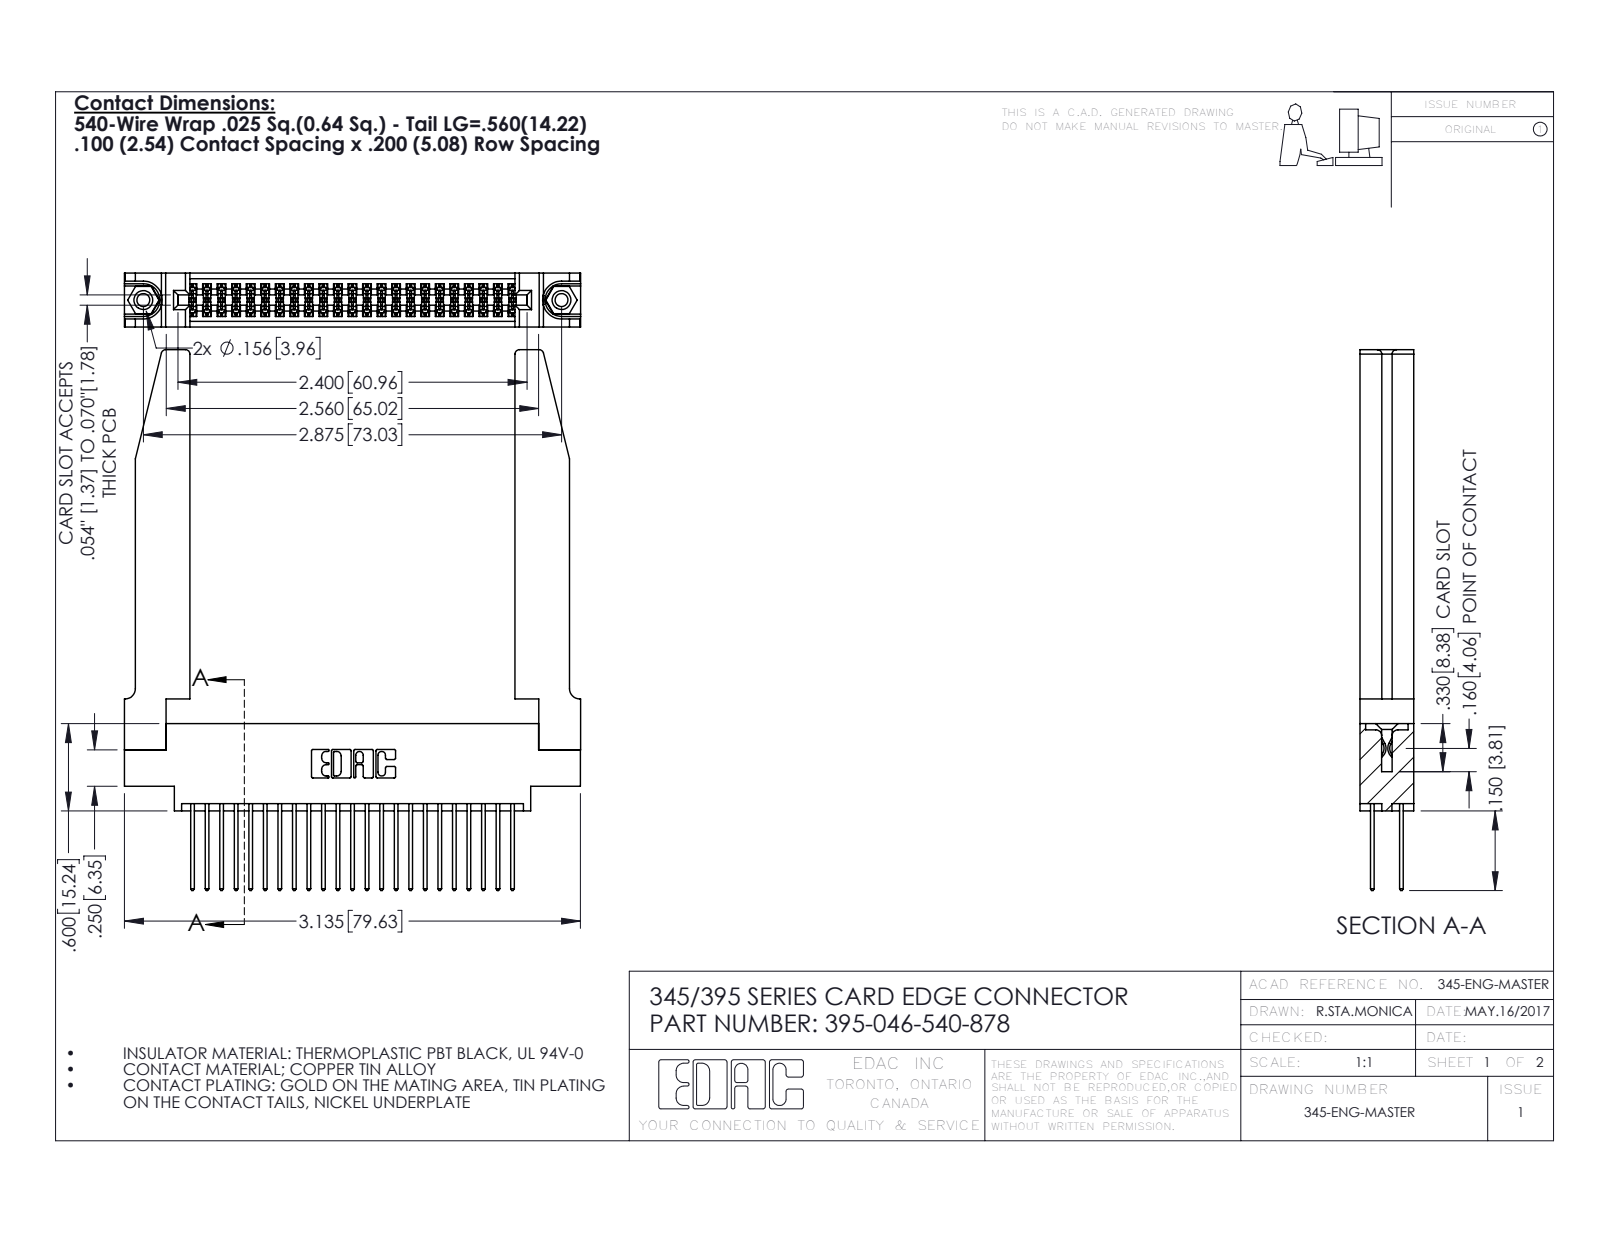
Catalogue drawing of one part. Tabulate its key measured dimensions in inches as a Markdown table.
| quantity | value |
| --- | --- |
| part name | 345-250-001_345-250-001-102; 395-046-540-878; 345-292-001_345-293-140; 345 Part_0.170 Offset - 0.156 Dia-TH (+1 more) |
| STEP written by | SolidWorks 2016 (CONFIG_CONTROL_DESIGN) |
| units | inches |
| bodies | 51 solids, 2664 faces (1744 planar, 868 cylindrical, 52 other) |
| overall size | 3.717 × 3.136 × 0.37 |
| volume | 0.939 in³ |
| surface area | 28.97 in² |
| round holes (diameter × count) | 0.089 × 2, 0.125 × 2, 0.156 × 2, 0.064 × 1 |
| round bosses / shafts (diameter × count) | 0.155 × 2 |
| partial cylindrical surfaces (radius × count) | 0.006 × 69, 0.01 × 46, 0.01 × 22, 0.03 × 8, 0.007 × 6, 0.031 × 6, 0.026 × 3, 0.014 × 2 |
| main face-to-face distances | 0.37, 0.072, 0.298, 0.098, 0.272, 0.025, 0.2, 0.225, 0.175, 0.148 |
| hole center spacings | 0.27, 2.641, 2.875 |
